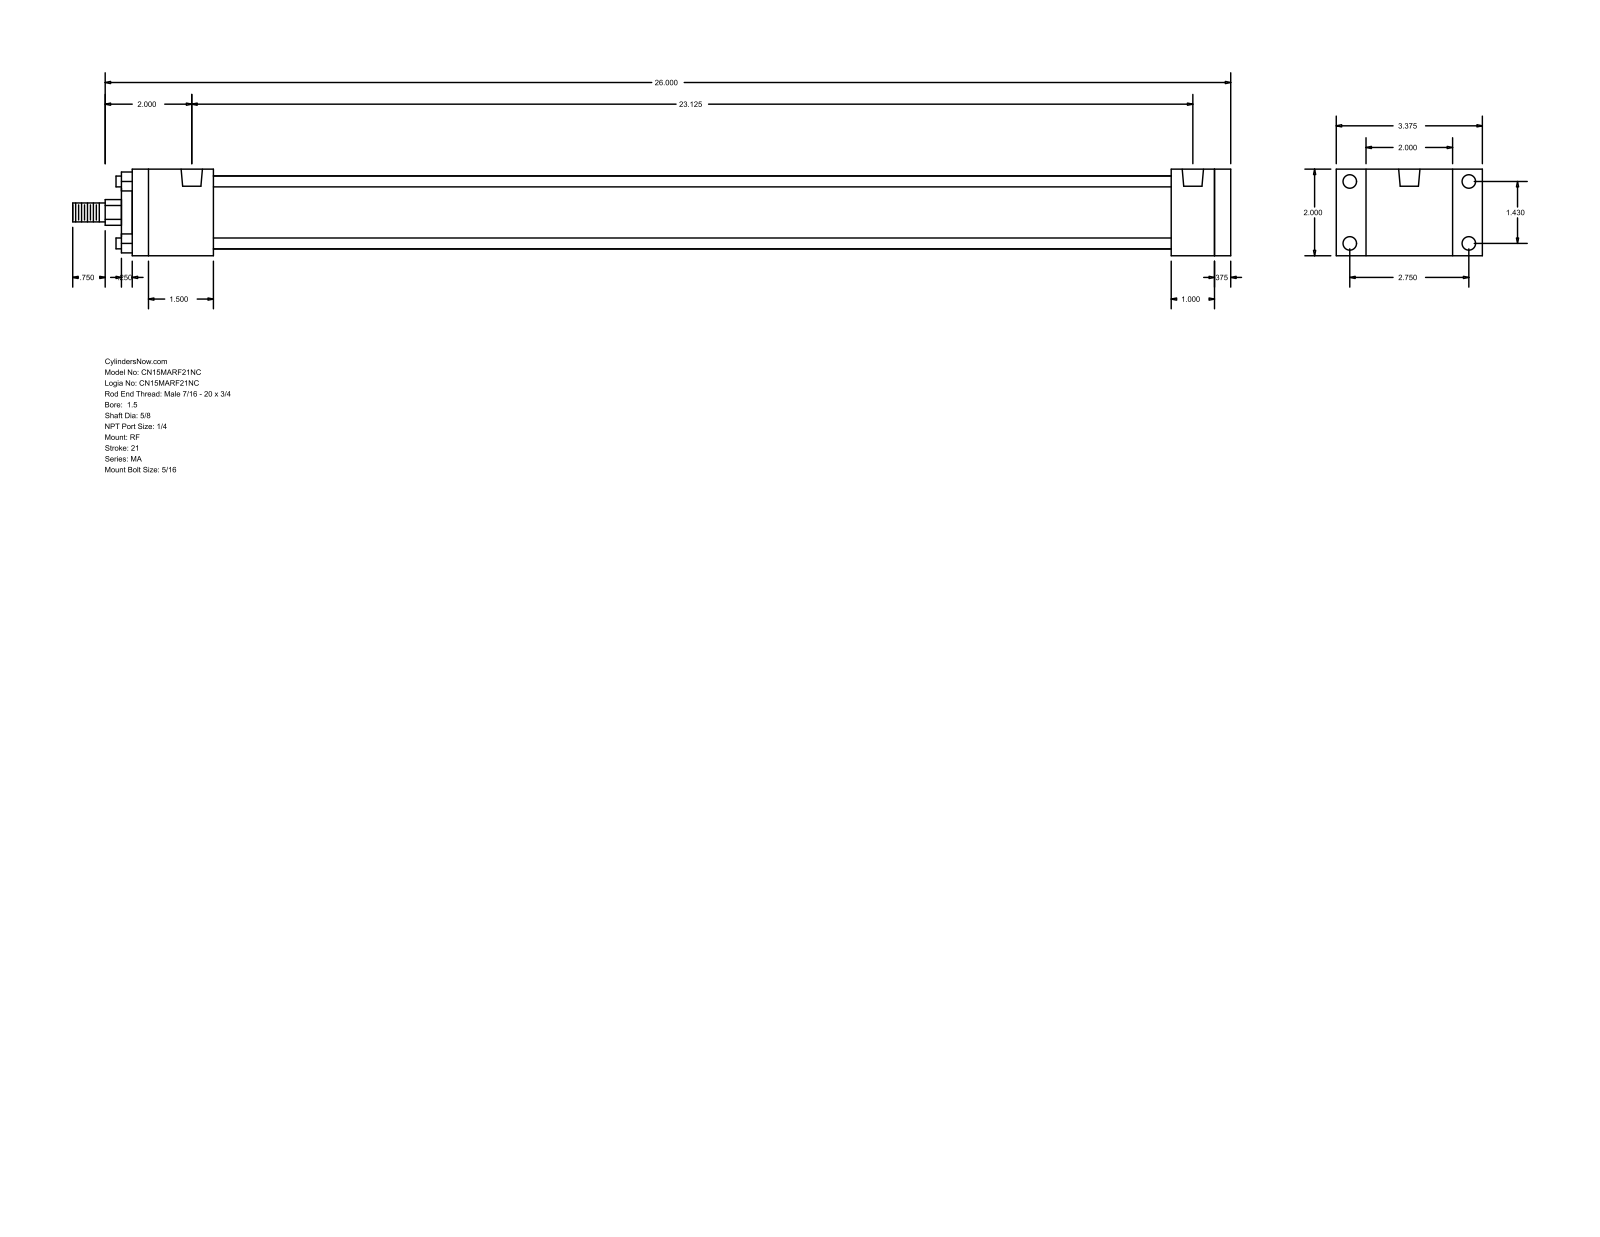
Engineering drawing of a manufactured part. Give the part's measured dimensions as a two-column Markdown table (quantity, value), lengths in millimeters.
| quantity | value |
| --- | --- |
| part name | MA_RF__0150_0.625 |
| STEP written by | GSSL Pune (CONFIG_CONTROL_DESIGN) |
| units | millimeters |
| bodies | 0 solids, 92 faces (64 planar, 28 cylindrical, 0 other) |
| overall size | 679.45 × 85.72 × 50.8 |
| round holes (diameter × count) | 7.94 × 8, 12.49 × 2 |
| round bosses / shafts (diameter × count) | 6.35 × 4, 42.93 × 1, 28.57 × 1, 15.88 × 1, 11.11 × 1 |
| partial cylindrical surfaces (radius × count) | 7.54 × 1 |
| main face-to-face distances | 50.8, 9.52, 635, 644.52, 25.4, 609.6, 34.92, 47.62, 561.98, 587.38 |
| hole center spacings | 36.32, 69.84, 78.72, 587.37 |
